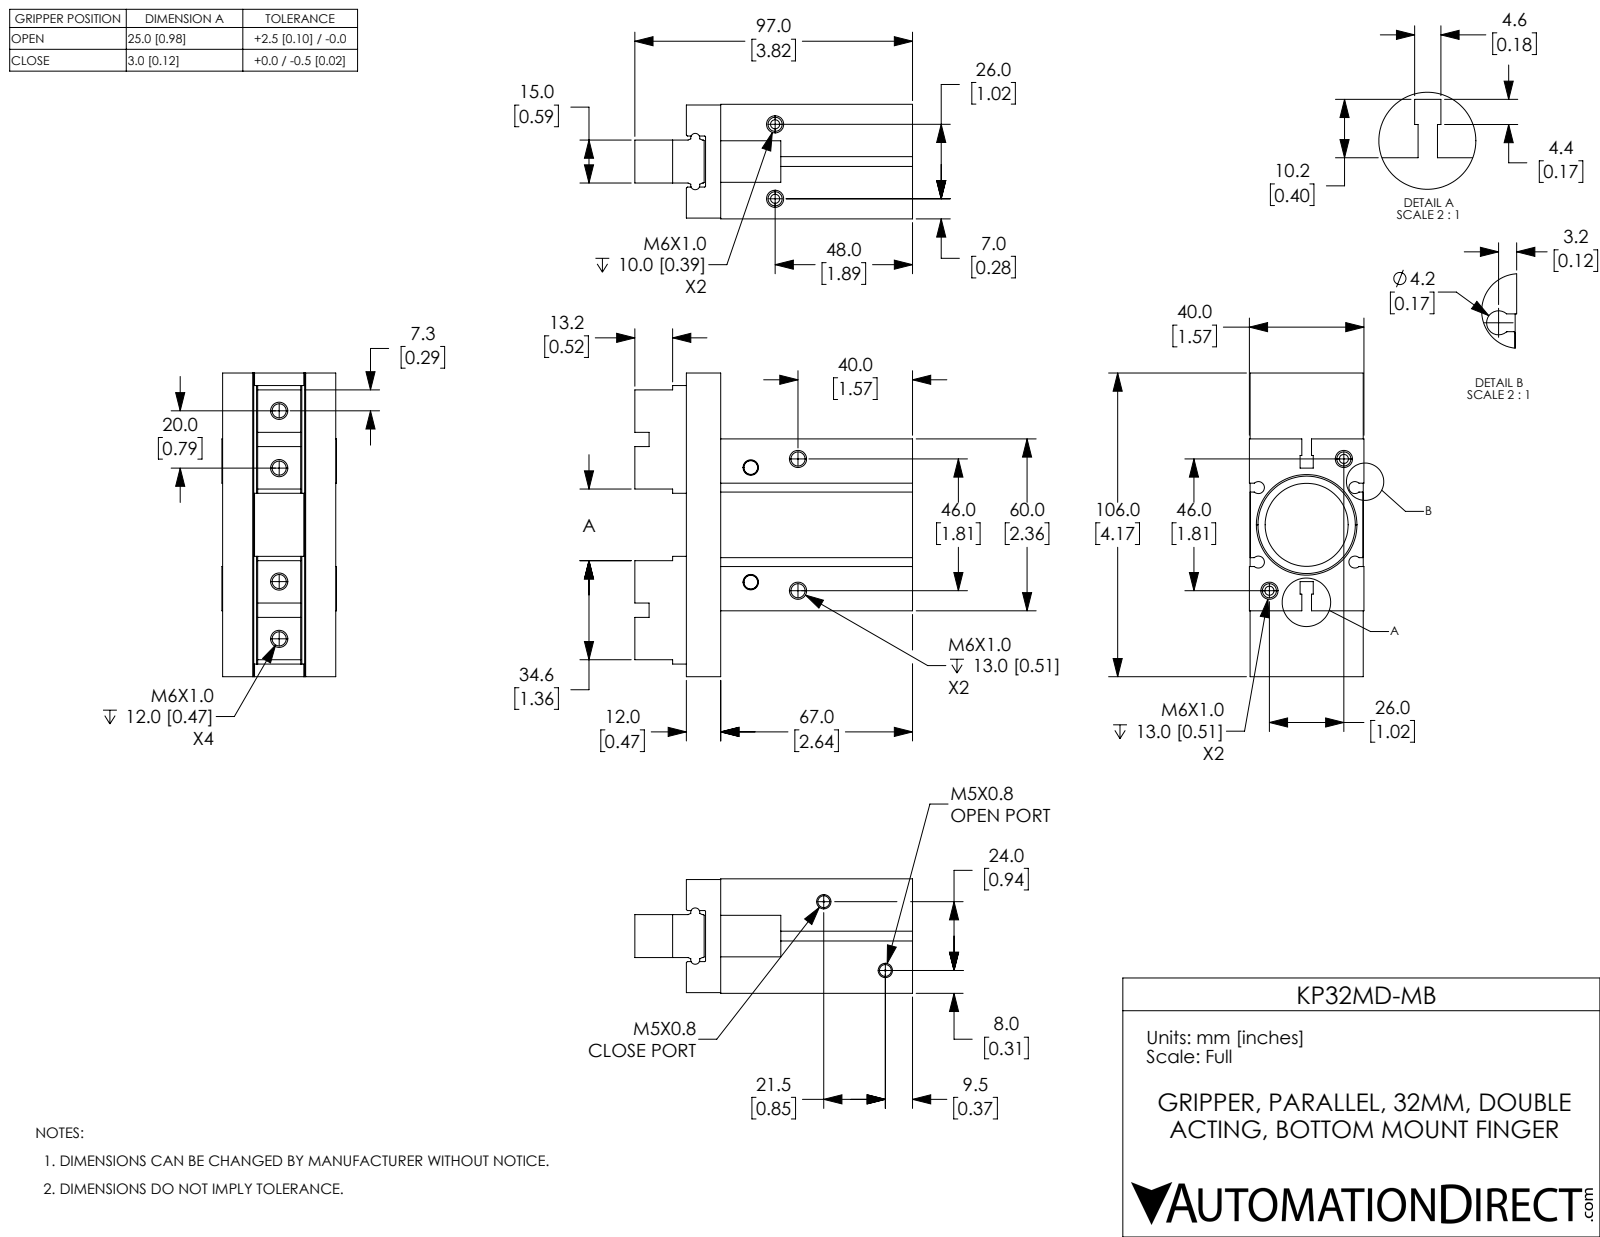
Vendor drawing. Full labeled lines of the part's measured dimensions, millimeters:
Part name (STEP PRODUCT): KP32MD-MB; KP32MD-MB-3; KP32MD-MB-2; KP32MD-MB-1
STEP written by: SolidWorks 2017 (CONFIG_CONTROL_DESIGN)
Units: millimetres
Bodies: 3 solids, 242 faces (126 planar, 62 cylindrical, 54 other)
Overall size (bounding box): 106 × 97 × 40
Volume: 189 520 mm³ · Surface area: 45 644 mm²
Round holes (diameter × count): ⌀4.92 ×4, ⌀0.5 ×2, ⌀4.13 ×2, ⌀4.92 ×2, ⌀6.02 ×2, ⌀29 ×1, ⌀34 ×1
Partial cylindrical surfaces — rounded edges, fillets, slot ends (radius × count): R0.2 ×6, R2.1 ×4, R2.46 ×4, R2.46 ×4, R0.3 ×2, R1.59 ×2
Main face-to-face distances: 12.5, 27.25, 39.7, 27.5, 12.2, 27.2, 12.75, 39.75, 12.25, 39.45
Hole centre spacings: 26.42, 17.03, 26, 30.23, 32.22, 38.51, 45.9, 46
